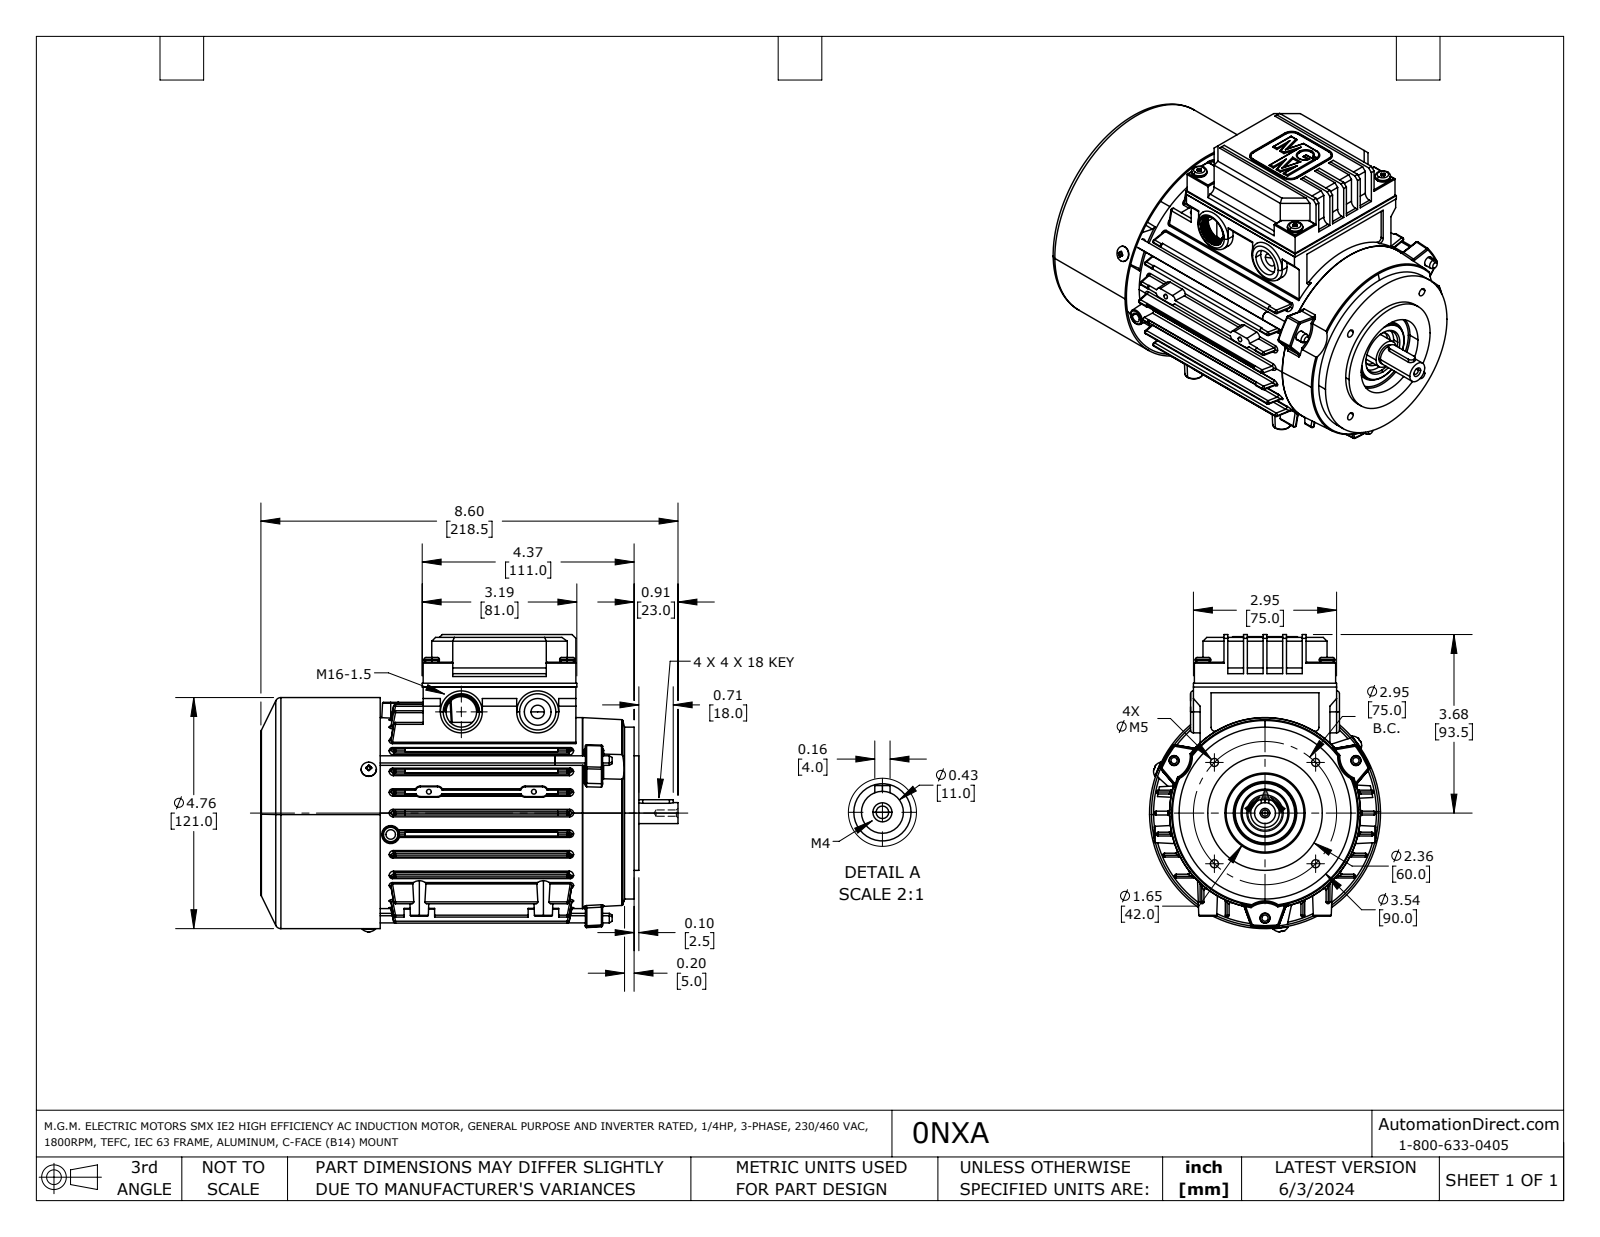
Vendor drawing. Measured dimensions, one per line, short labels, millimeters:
name: 0NXA
written by: SolidWorks 2021 (AUTOMOTIVE_DESIGN)
unit: mm
bodies: 21 solids, 3139 faces (1062 planar, 1019 cylindrical, 1058 other)
size: 218.5 × 155.7 × 121
volume: 476 500 mm³; area: 306 700 mm²
holes: 12× ⌀3, 8× ⌀3.3, 7× ⌀4, 7× ⌀5.5, 6× ⌀5, 4× ⌀4.2, 3× ⌀3.2, 3× ⌀7, 2× ⌀2.5, 2× ⌀16, 1× ⌀8, 1× ⌀14
bosses: 10× ⌀3, 7× ⌀8, 4× ⌀3.5, 3× ⌀5, 3× ⌀2, 1× ⌀121, 1× ⌀100, 1× ⌀95
rounds: 281× R1, 36× R0.4, 36× R0.5, 32× R0.2, 16× R0.1, 16× R0.8, 12× R0.4, 12× R0.6
face distances: 2, 22, 11, 24, 33, 13, 1.5, 3.5, 20, 9
hole spacings: 94.4, 11.5, 11.6, 13.7, 19.5, 28.5, 30.8, 31
